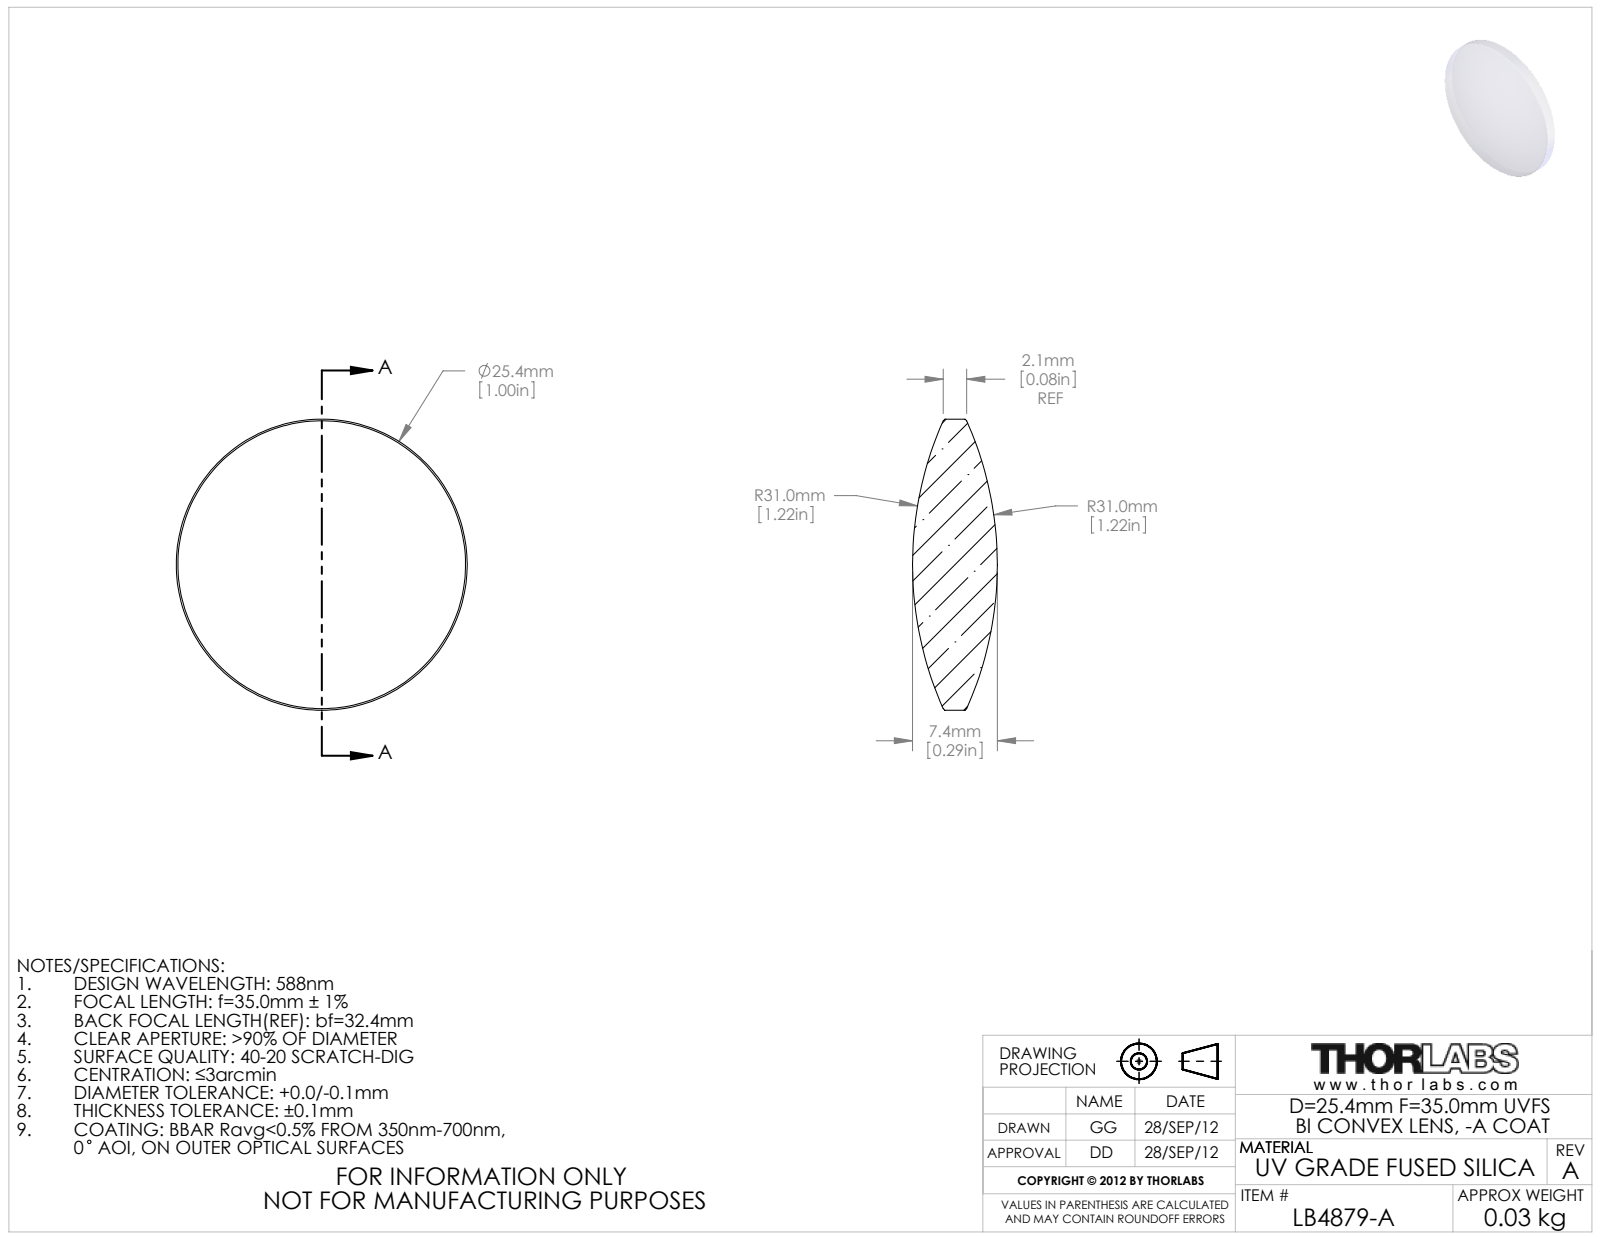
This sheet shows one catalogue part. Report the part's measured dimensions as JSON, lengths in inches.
{"part_name": "25014-E0W", "step_written_by": "SolidWorks 2011 (CONFIG_CONTROL_DESIGN)", "units": "inches", "bodies": {"solids": 1, "faces": 10, "planar": 0, "cylindrical": 2, "other": 8}, "overall_size": [1, 1, 0.291], "volume_in3": 0.145, "surface_area_in2": 1.874, "round_bosses_or_shafts": [[1, 1]]}
